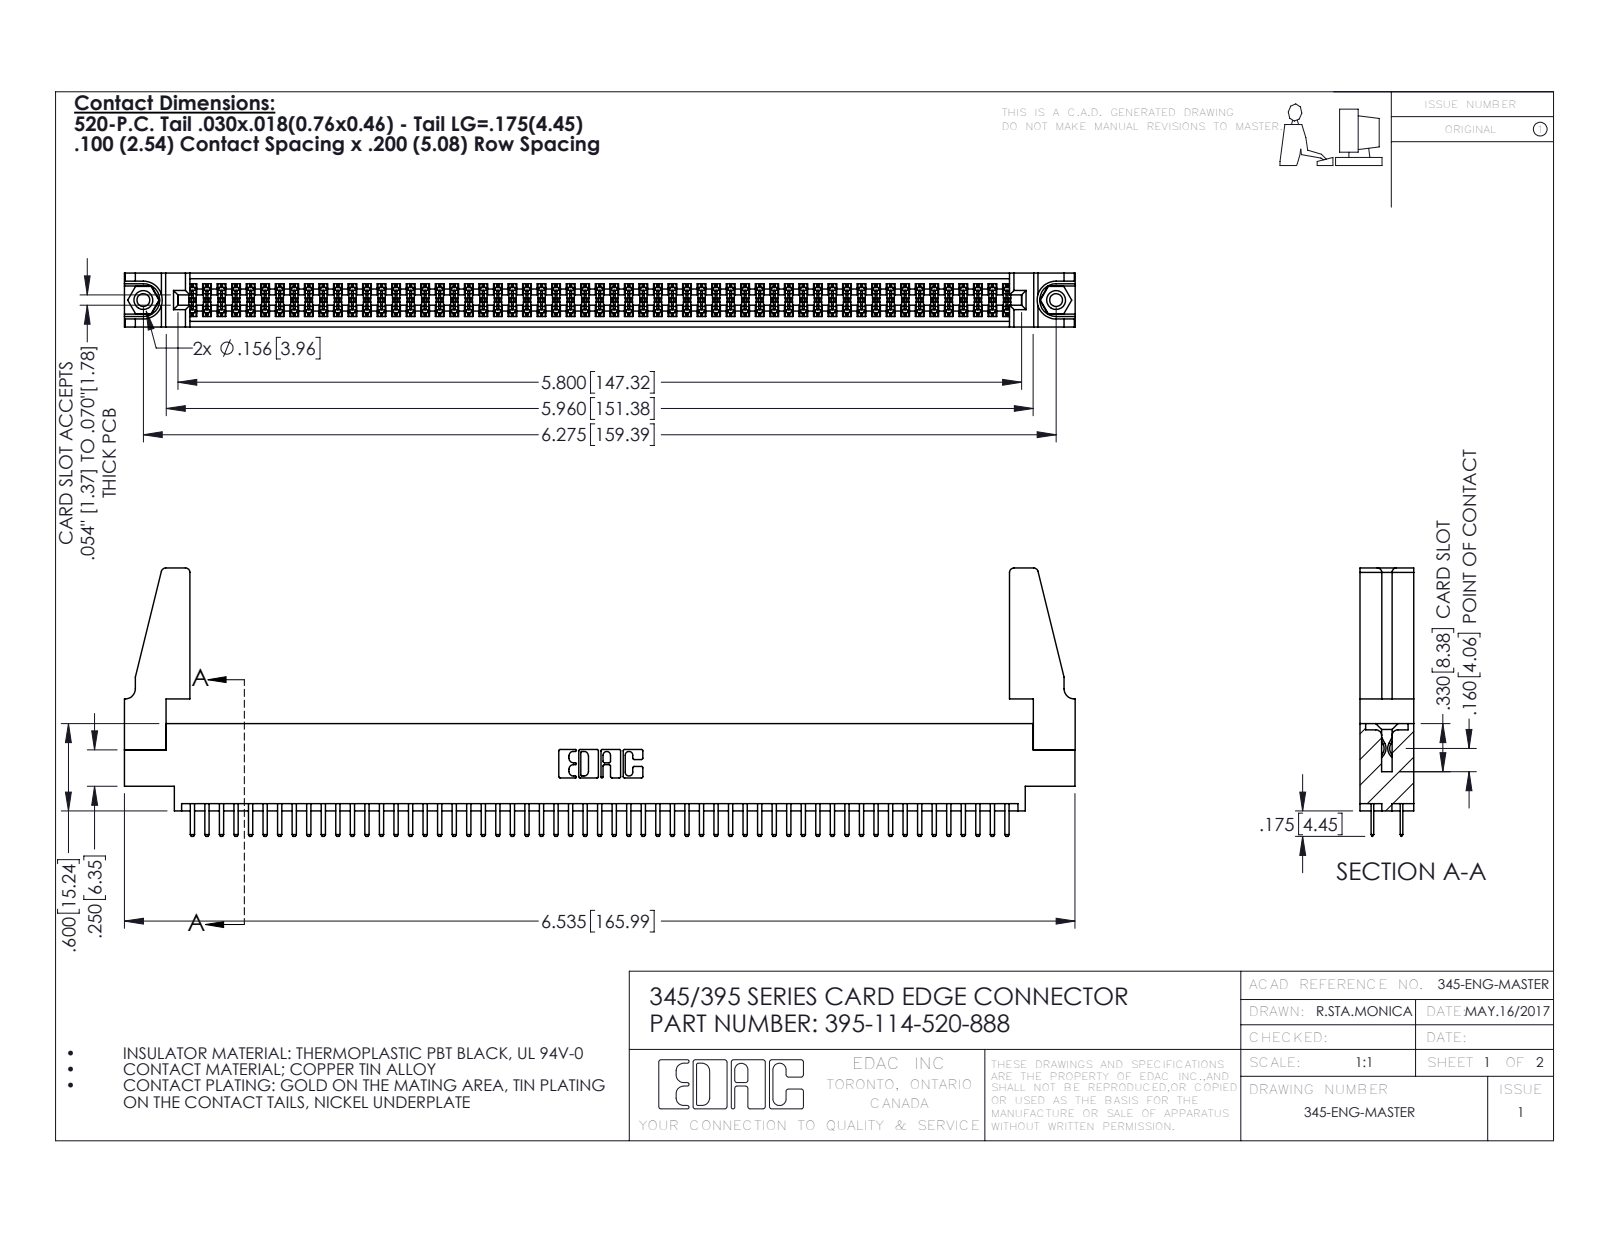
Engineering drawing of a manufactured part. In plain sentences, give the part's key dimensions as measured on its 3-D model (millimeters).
The part is named "345-250-001_345-250-001-102; 345-292-001_345-293-120; 345 Part_0.170 Offset - 0.156 Dia-TH; 395-114-520-888 (+1 more)". Its 3-D file was written by "SolidWorks 2016 (CONFIG_CONTROL_DESIGN)". It is 119 solids with 6410 faces: 4146 planar, 2248 cylindrical and 16 other. Overall it measures 166 by 46.9 by 9.4 millimeters. Its volume is 19 350 cubic millimeters and its surface area 27 250 square millimeters. Round holes: 2 of diameter 2.3, 2 of diameter 3.2, 2 of diameter 4, 1 of diameter 1.6. Round bosses or shafts: 2 of diameter 3.9. Partial cylindrical surfaces (rounded edges, fillets, slot ends): 171 of radius 0.2, 118 of radius 0.3, 22 of radius 0.3, 8 of radius 0.8, 6 of radius 0.2, 6 of radius 0.8, 3 of radius 0.7, 2 of radius 0.4. The main face-to-face distances are 1.8, 7.6, 9.4, 5.1, 2.5, 6.9, 0.6, 5.7, 0.6, 1.8. The hole center spacings are 6.9, 153.4, 159.4.
